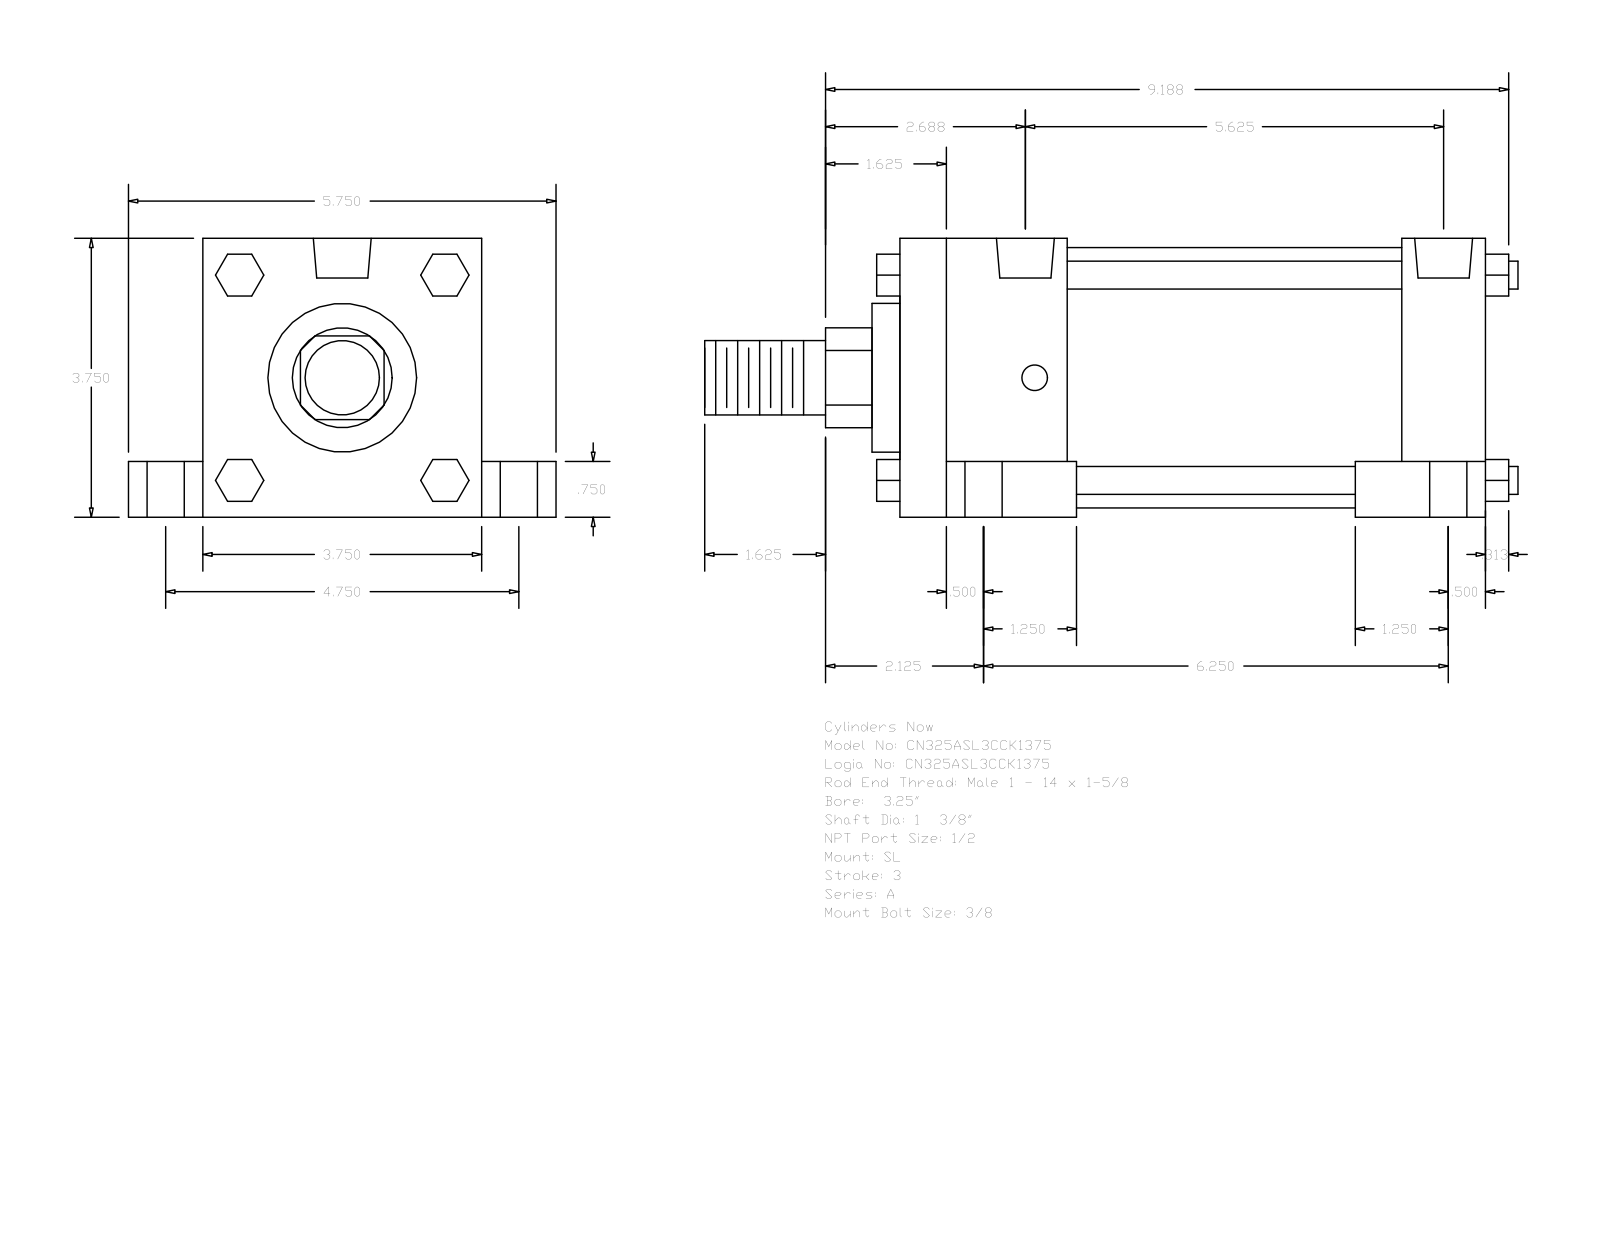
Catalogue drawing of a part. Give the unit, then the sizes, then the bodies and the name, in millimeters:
Units: millimetres
Overall size (bounding box): 277.81 × 146.05 × 95.25
Round holes (diameter × count): ⌀8.73 ×4, ⌀12.7 ×4, ⌀19.05 ×4, ⌀19.77 ×2
Round bosses / shafts (diameter × count): ⌀9.53 ×4, ⌀88.9 ×1, ⌀50.8 ×1, ⌀34.92 ×1, ⌀25.4 ×1
Partial cylindrical surfaces — rounded edges, fillets, slot ends (radius × count): R17.06 ×1
Main face-to-face distances: 95.24, 200.03, 25.41, 120.65, 19.05, 76.19, 57.15, 28.58, 171.45, 114.3
Hole centre spacings: 3.18, 60.35, 60.52, 62, 62.81, 120.66, 136.52, 139.7
Bodies: 0 solids, 150 faces (114 planar, 36 cylindrical, 0 other)
Part name (STEP PRODUCT): A_SL__0325_1.375
STEP written by: GSSL Pune (CONFIG_CONTROL_DESIGN)
